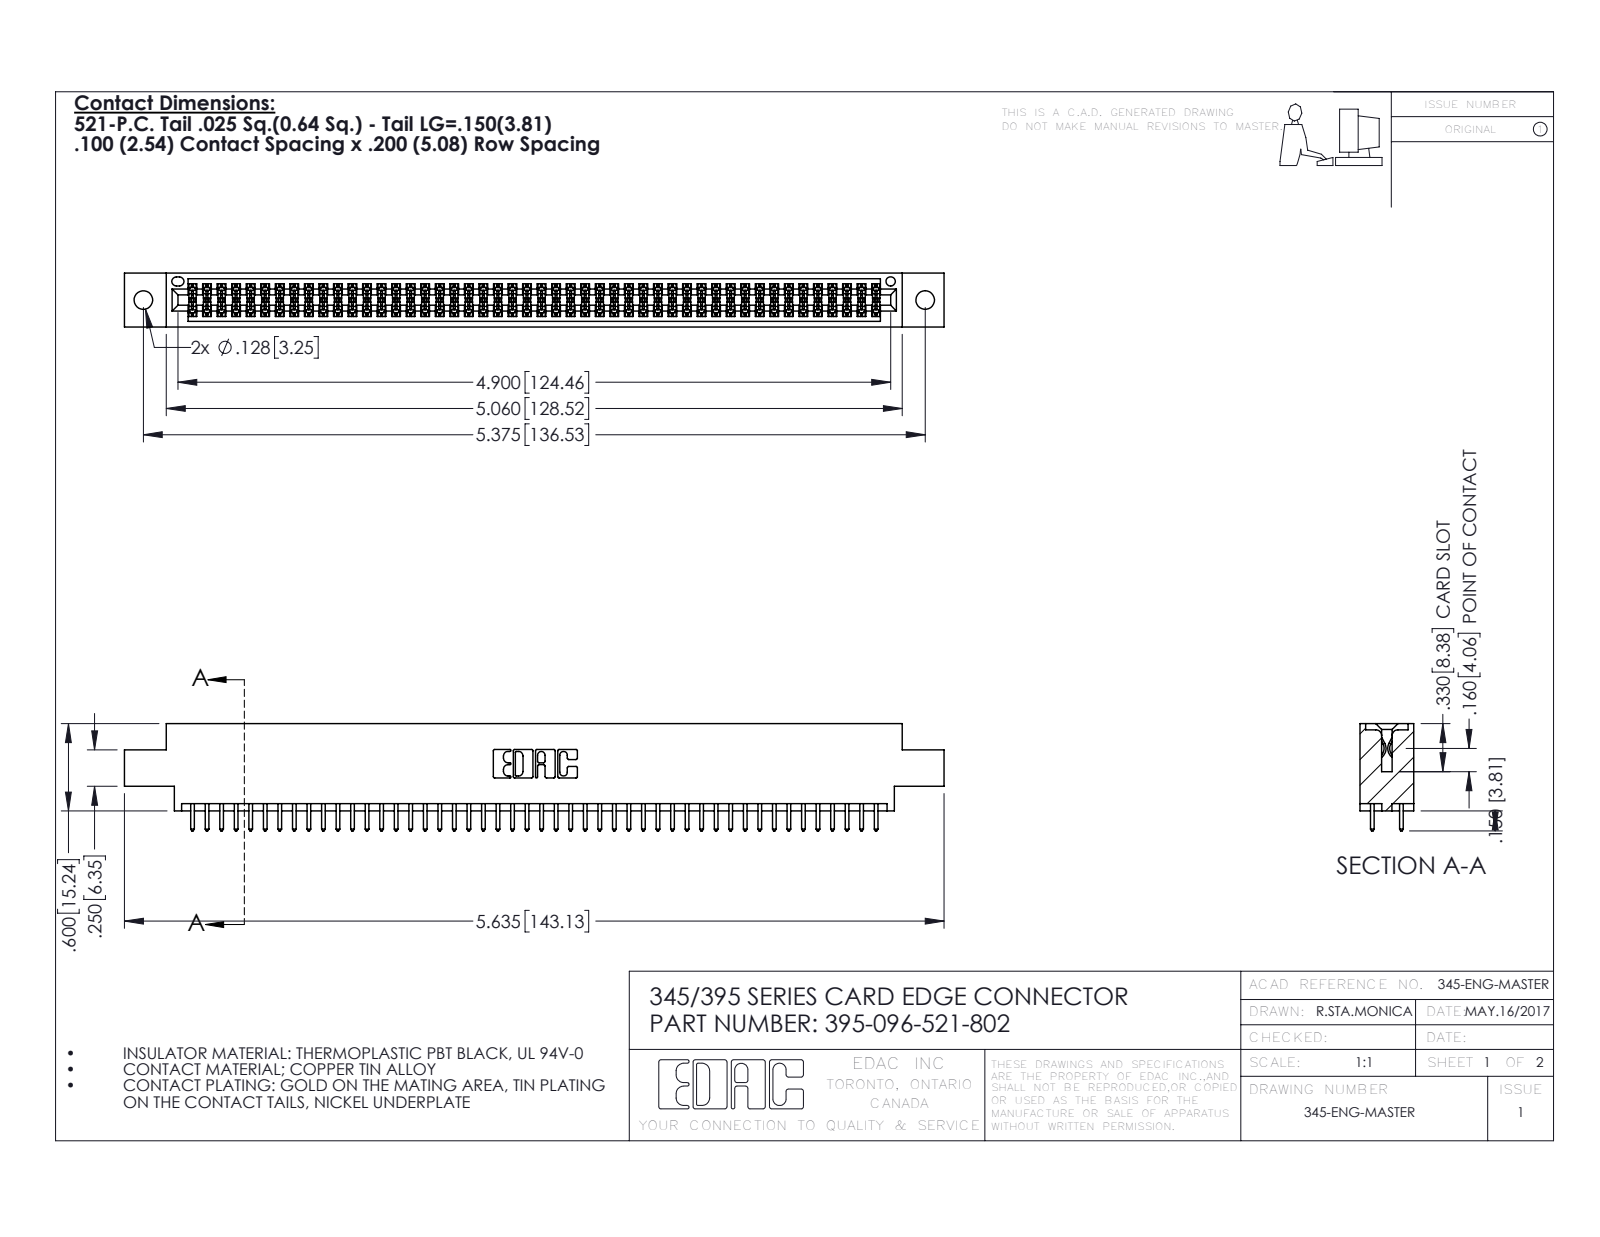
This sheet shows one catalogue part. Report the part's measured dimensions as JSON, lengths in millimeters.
{"part_name": "395-096-521-802; 345-292-001_345-293-121; 345 Part_0.170 Offset - 0.128 Dia", "step_written_by": "SolidWorks 2016 (CONFIG_CONTROL_DESIGN)", "units": "millimeters", "bodies": {"solids": 97, "faces": 4930, "planar": 3252, "cylindrical": 1678, "other": 0}, "overall_size": [143.1, 18.7, 9.4], "volume_mm3": 13800, "surface_area_mm2": 20080, "round_holes": [[3.3, 2], [1.6, 1]], "partial_cylinders_radius": [[0.2, 144], [0.3, 96], [0.3, 22], [0.2, 6], [0.8, 6], [0.7, 3], [0.4, 2], [0.5, 2]], "face_to_face_distances": [1.8, 7.6, 9.4, 5.1, 2.5, 6.9, 0.6, 5.7, 4.4, 3.8], "hole_center_spacings": [6.9, 130.5, 136.5]}
